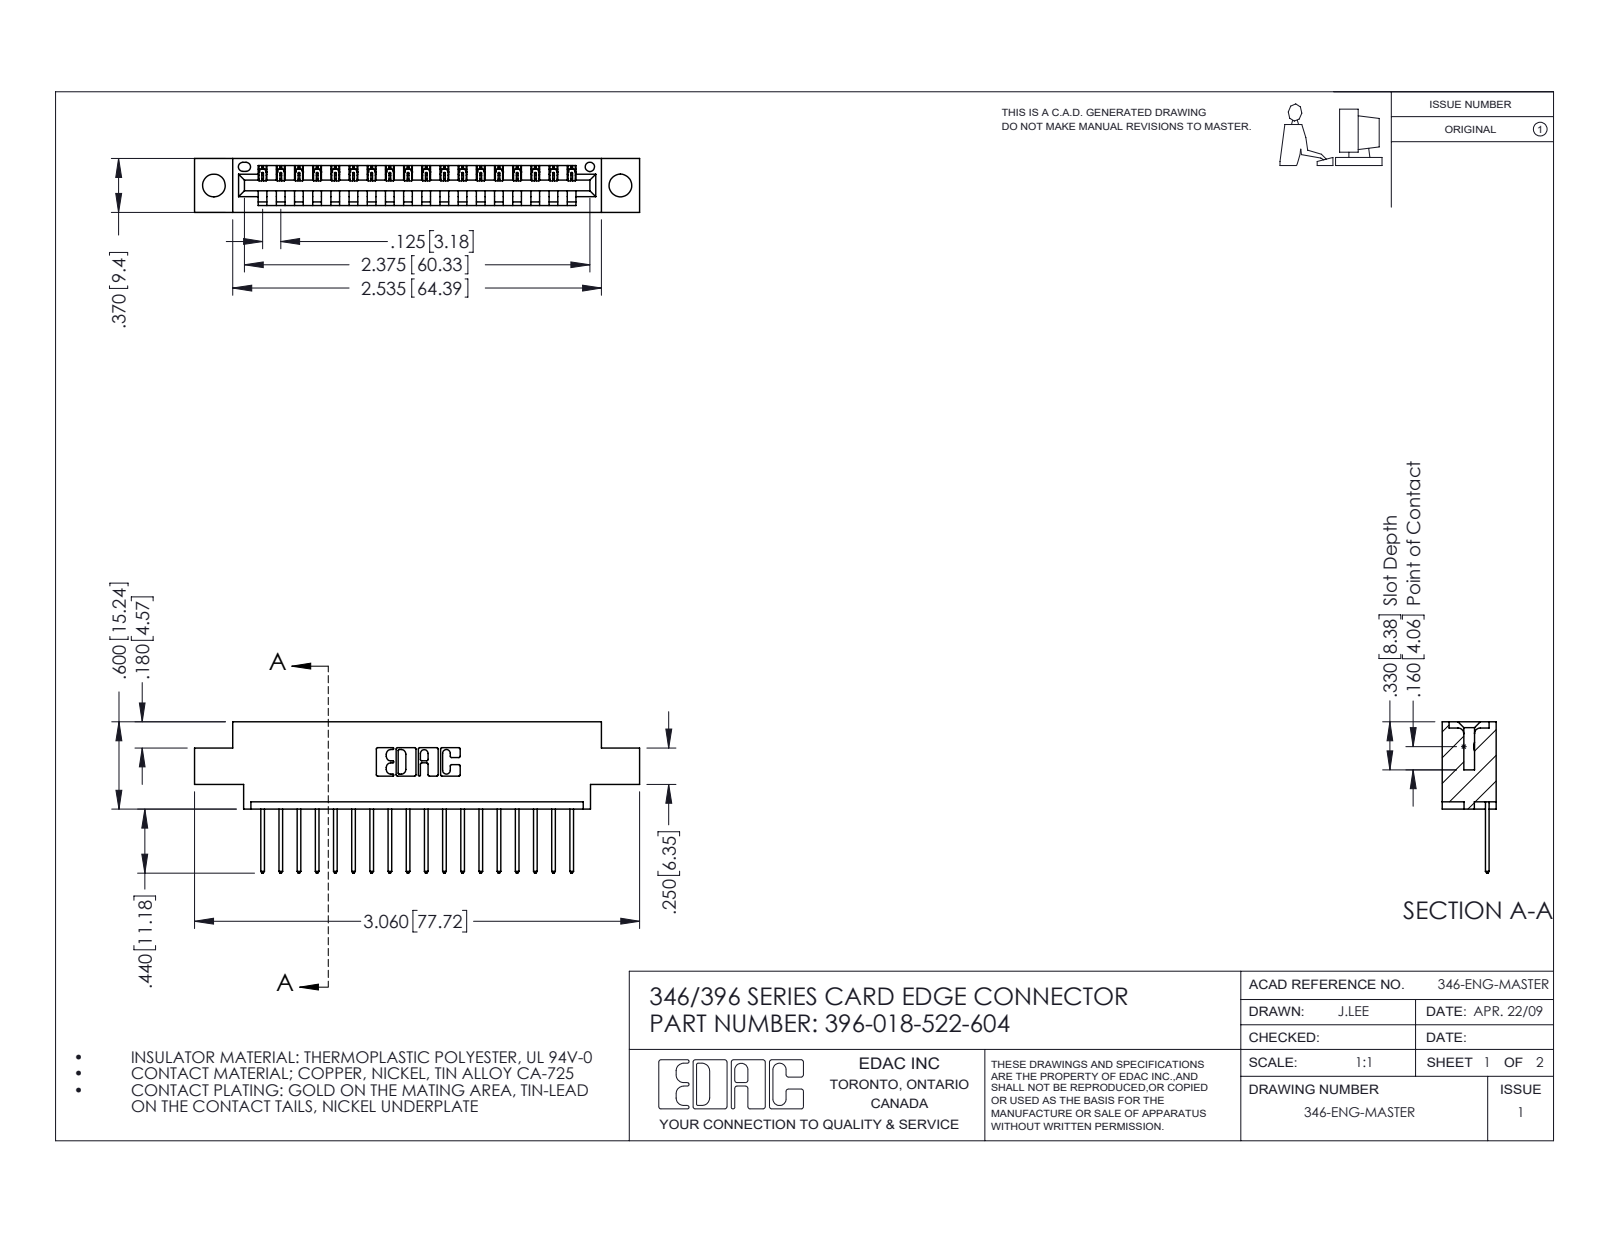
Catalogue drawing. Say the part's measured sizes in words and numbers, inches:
The part is named "346 Part_0.170 Offset - 0.156 Dia-TH; 345-292-001_345-293-122; 396-018-522-604". Its 3-D file was written by "SolidWorks 2016 (CONFIG_CONTROL_DESIGN)". It is 19 solids with 1170 faces: 800 planar, 370 cylindrical and 0 other. Overall it measures 3.06 by 1.04 by 0.37 inches. Its volume is 0.429 cubic inches and its surface area 13.28 square inches. Round holes: 2 of diameter 0.156, 1 of diameter 0.064. Partial cylindrical surfaces (rounded edges, fillets, slot ends): 36 of radius 0.006, 36 of radius 0.01, 22 of radius 0.01, 6 of radius 0.007, 6 of radius 0.031, 3 of radius 0.026, 2 of radius 0.031, 2 of radius 0.04. The main face-to-face distances are 0.048, 0.322, 0.37, 0.25, 0.072, 0.298, 0.025, 0.148, 0.222, 0.1. The hole center spacings are 0.246, 2.588, 2.795.
